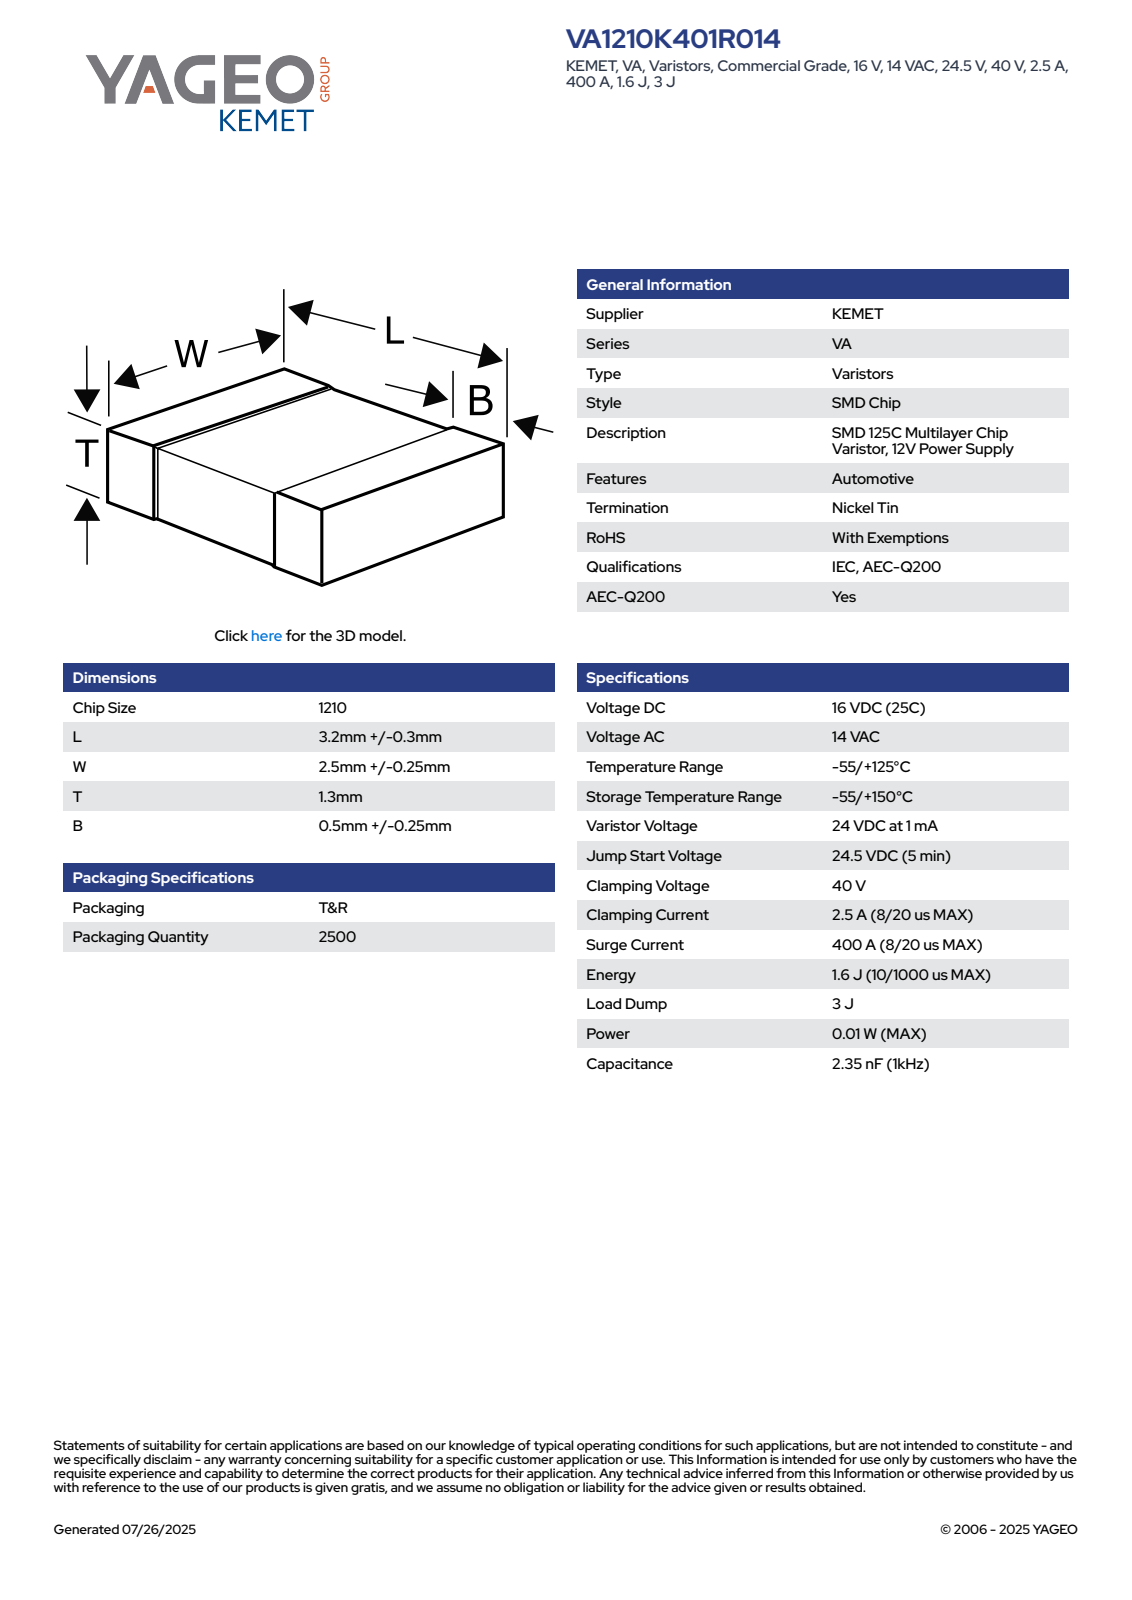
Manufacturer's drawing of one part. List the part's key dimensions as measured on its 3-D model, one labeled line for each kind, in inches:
Part name (STEP PRODUCT): VS_SMD_1210_L3.50W2.75T1.3B0.75
STEP written by: SolidWorks 2014 (AUTOMOTIVE_DESIGN)
Units: inches
Bodies: 4 solids, 125 faces (71 planar, 38 cylindrical, 16 other)
Overall size (bounding box): 0.138 × 0.108 × 0.051
Volume: 0.001 in³ · Surface area: 0.054 in²
Main face-to-face distances: 0.049, 0.046, 0.051, 0.138, 0.106, 0.104, 0.108, 0.049, 0.047, 0.059
